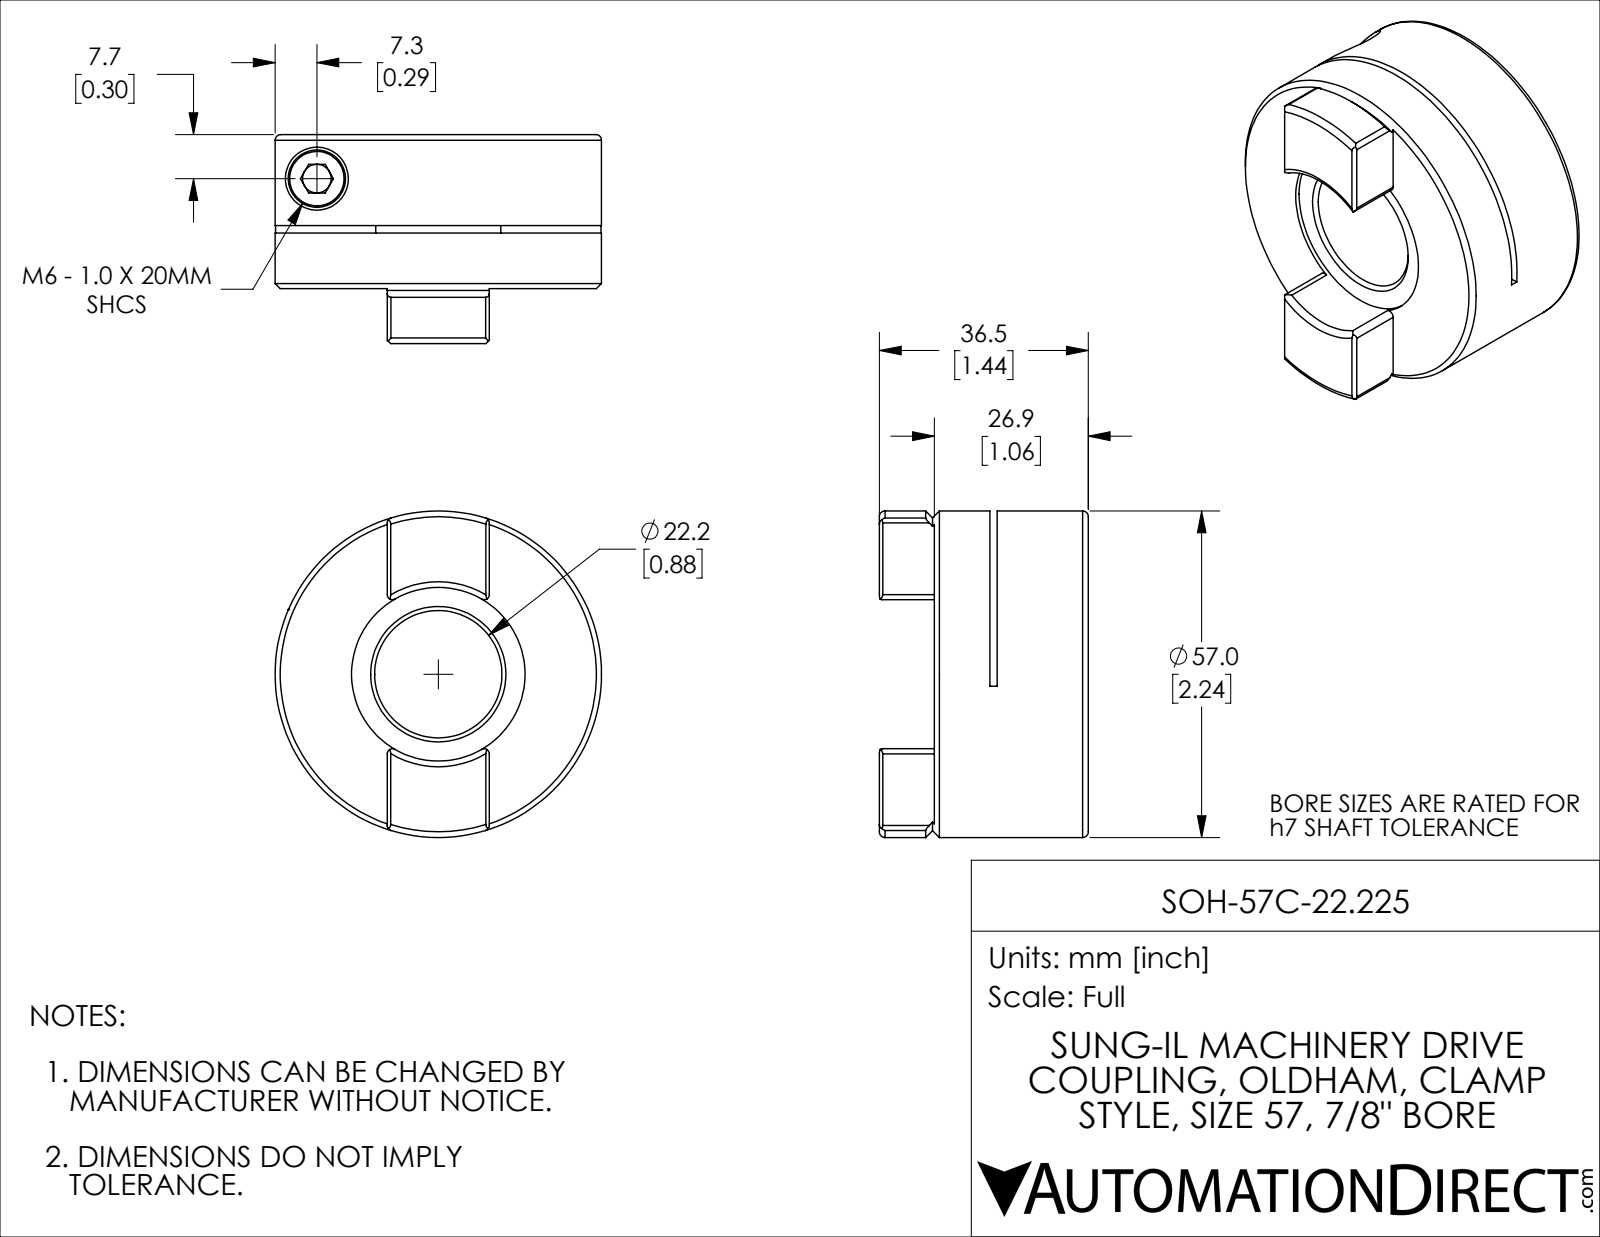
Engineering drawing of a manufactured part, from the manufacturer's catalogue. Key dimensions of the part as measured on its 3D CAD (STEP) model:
Part name (STEP PRODUCT): SOH-57C-22.225
STEP written by: SolidWorks 2021 (CONFIG_CONTROL_DESIGN)
Units: inches
Bodies: 2 solids, 99 faces (39 planar, 33 cylindrical, 27 other)
Overall size (bounding box): 2.244 × 2.244 × 1.437
Volume: 3.64 in³ · Surface area: 25.21 in²
Round holes (diameter × count): ⌀0.197 ×1, ⌀0.252 ×1, ⌀0.433 ×1, ⌀0.875 ×1, ⌀1.193 ×1
Round bosses / shafts (diameter × count): ⌀2.244 ×1, ⌀0.394 ×1, ⌀0.236 ×1
Partial cylindrical surfaces — rounded edges, fillets, slot ends (radius × count): R0.035 ×8, R1.575 ×1
Main face-to-face distances: 0.051, 1.059, 0.677, 0.382, 0.626, 0.433, 1.437, 0.811, 0.76, 0.378
